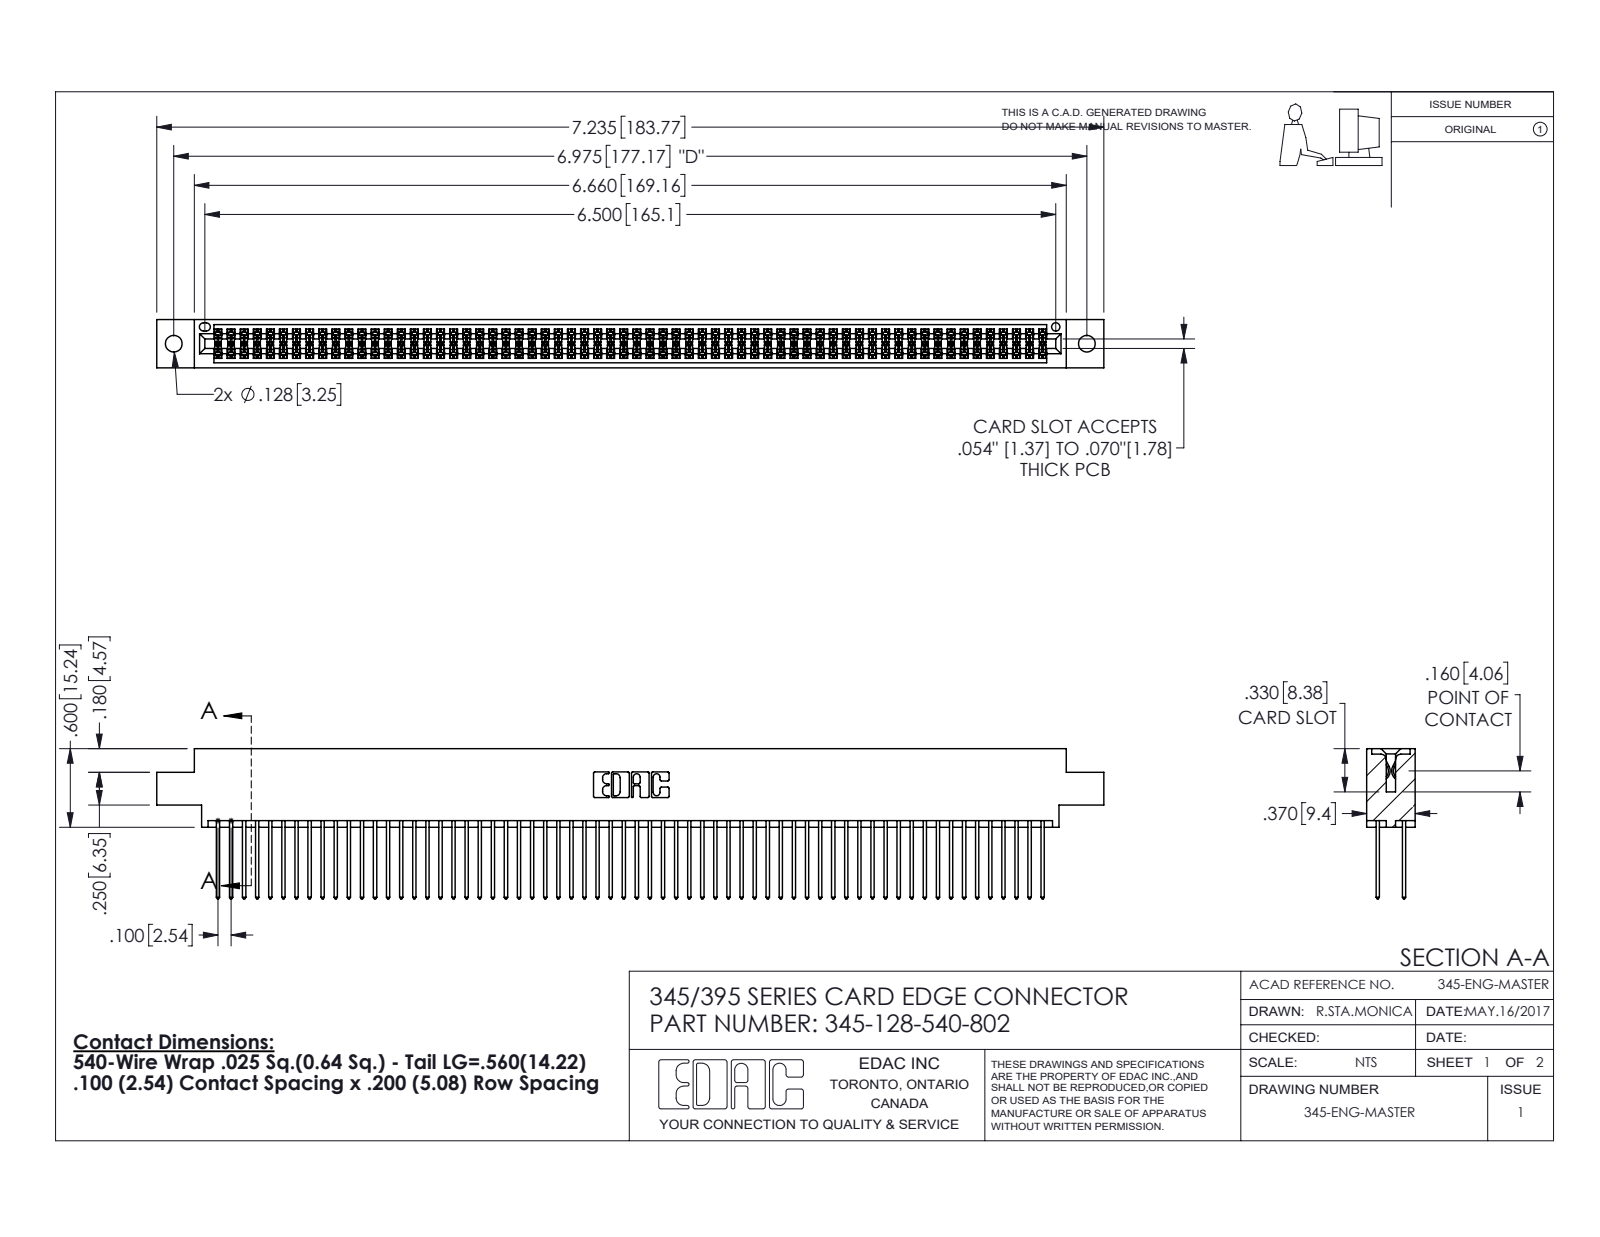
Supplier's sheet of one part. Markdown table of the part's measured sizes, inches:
| quantity | value |
| --- | --- |
| part name | 345-292-001_345-293-140; 345-128-540-802; 345 Part_0.170 Offset - 0.128 Dia |
| STEP written by | SolidWorks 2016 (CONFIG_CONTROL_DESIGN) |
| units | inches |
| bodies | 129 solids, 6530 faces (4308 planar, 2222 cylindrical, 0 other) |
| overall size | 7.235 × 1.147 × 0.37 |
| volume | 1.122 in³ |
| surface area | 46.09 in² |
| round holes (diameter × count) | 0.128 × 2, 0.064 × 1 |
| partial cylindrical surfaces (radius × count) | 0.006 × 192, 0.01 × 128, 0.01 × 22, 0.007 × 6, 0.031 × 6, 0.026 × 3, 0.014 × 2, 0.019 × 2 |
| main face-to-face distances | 0.298, 0.072, 0.2, 0.098, 0.272, 0.025, 0.37, 0.225, 0.175, 0.149 |
| hole center spacings | 0.27, 6.739, 6.975 |
